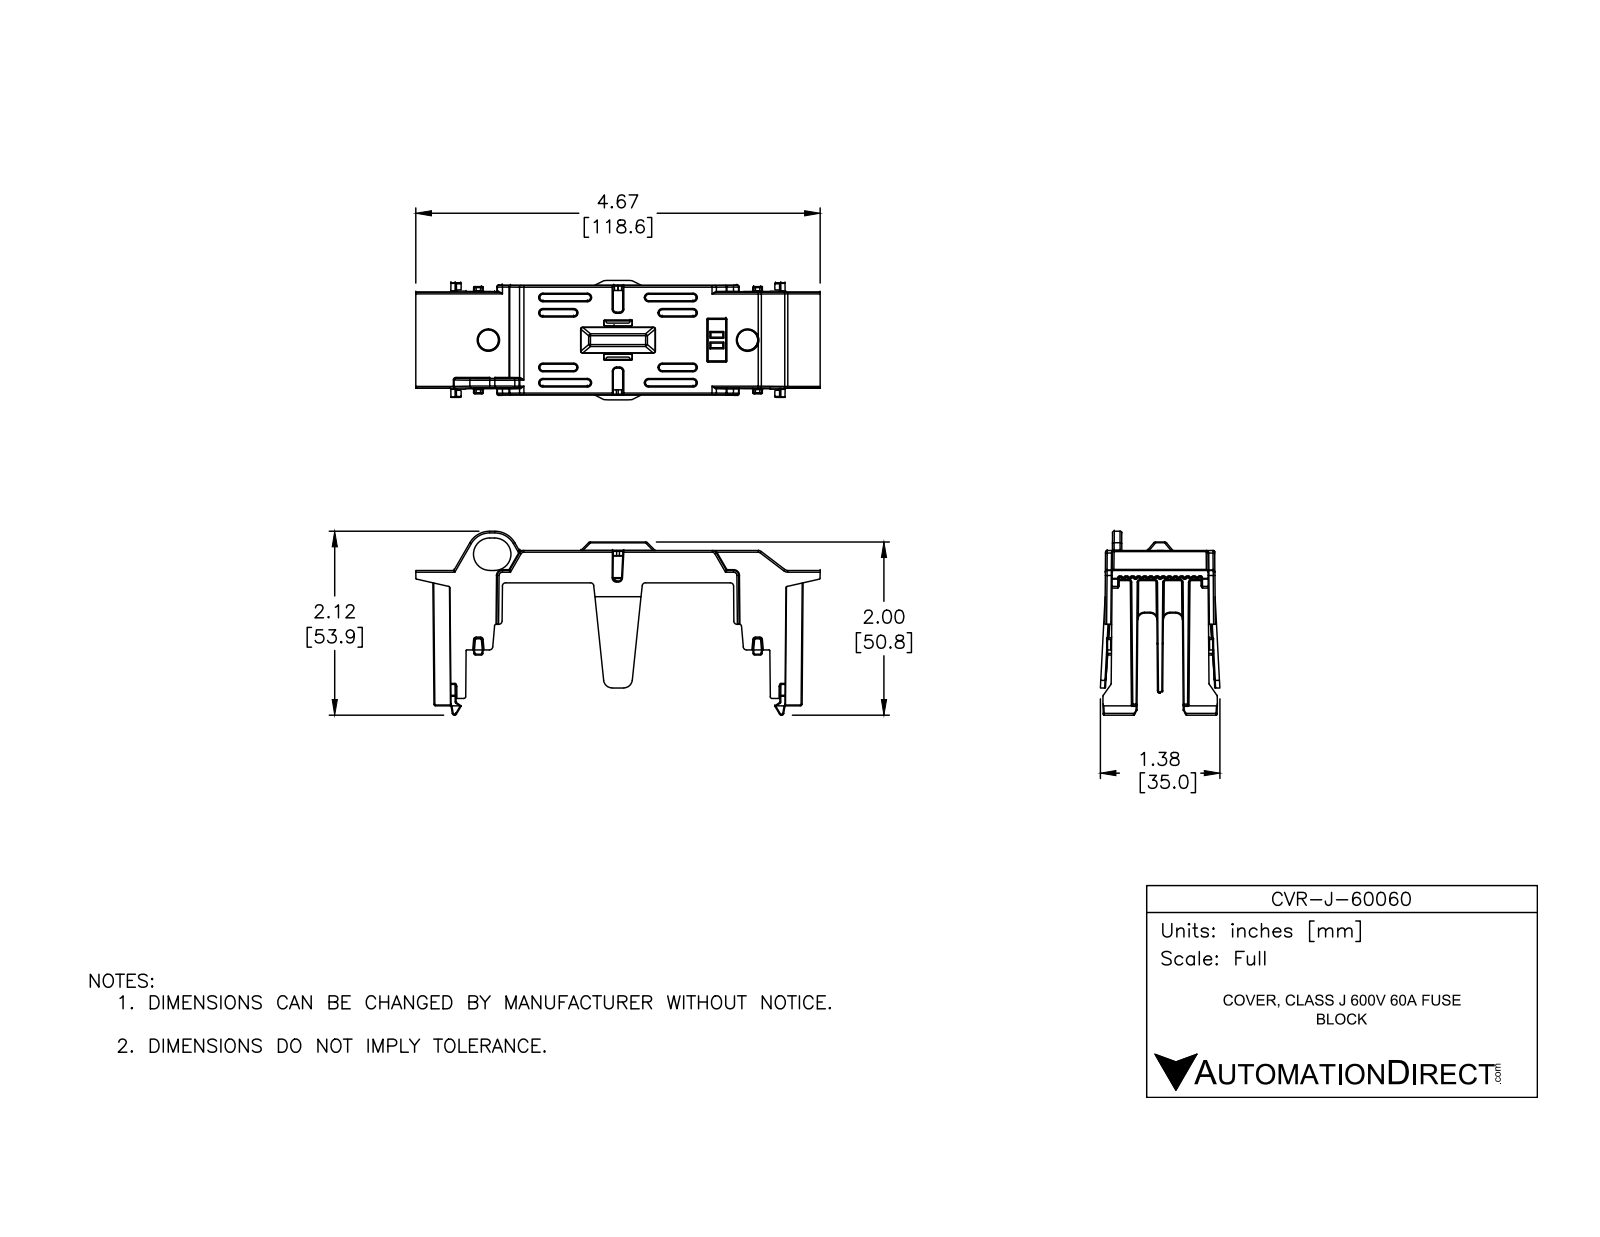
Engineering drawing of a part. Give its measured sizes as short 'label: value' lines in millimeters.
name: CVR-J-60060
written by: SolidWorks 2016 (AUTOMOTIVE_DESIGN)
unit: mm
bodies: 1 solid, 2426 faces (446 planar, 1066 cylindrical, 914 other)
size: 118.6 × 53.9 × 35.1
volume: 16 450 mm³; area: 22 120 mm²
rounds: 358× R0.3, 177× R0.2, 72× R0.5, 58× R1, 27× R0.1, 23× R0.8, 6× R1.5, 4× R2
face distances: 1.5, 2, 1.5, 5.8, 3.5, 96.7, 4.3, 0.5, 6.1, 7.6
